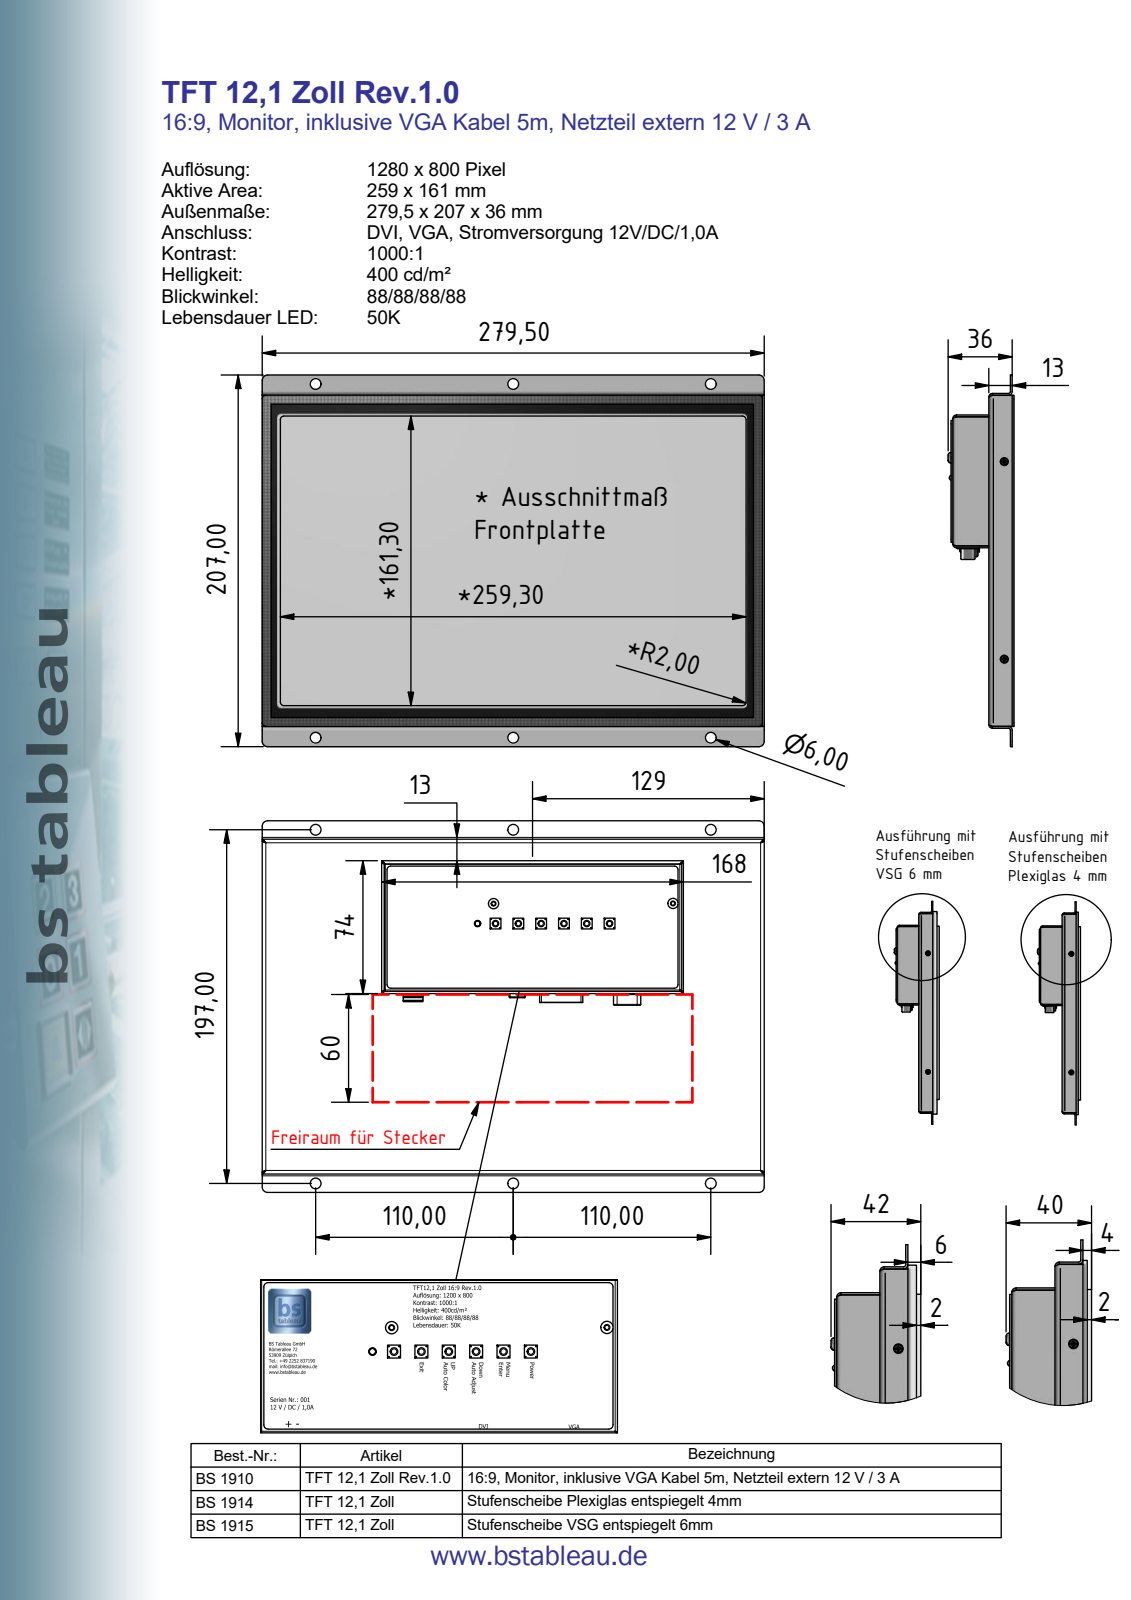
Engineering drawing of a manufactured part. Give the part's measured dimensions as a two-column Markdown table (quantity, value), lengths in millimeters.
| quantity | value |
| --- | --- |
| part name | 20000021 TFT 12,1 Zoll 16_9 Rev.1.0; 00003462 TDS 3165 - G121-1-L01 - MSC; 00000010 NB-4pol; 00000089 G121I1-L01 (+8 more) |
| STEP written by | Autodesk Inventor 2019 (AUTOMOTIVE_DESIGN) |
| units | millimeters |
| bodies | 72 solids, 2006 faces (1241 planar, 442 cylindrical, 323 other) |
| overall size | 279.5 × 207 × 36.65 |
| volume | 660 002 mm³ |
| surface area | 329 929 mm² |
| round holes (diameter × count) | 0.8 × 15, 2.46 × 12, 3.2 × 8, 5.41 × 8, 6 × 7, 1.57 × 2, 2.5 × 2, 2.6 × 2, 3.3 × 2, 3.4 × 2, 3.5 × 1 |
| round bosses / shafts (diameter × count) | 0.5 × 24, 3 × 9, 5.7 × 8, 5.42 × 8, 3.5 × 6, 8 × 2, 3.8 × 2, 2 × 2 |
| partial cylindrical surfaces (radius × count) | 0.1 × 172, 2 × 22, 0.5 × 20, 1 × 16, 4 × 16, 0.2 × 6, 0.8 × 6, 1.8 × 6 |
| main face-to-face distances | 1, 12, 10.5, 13, 2.5, 1.5, 21, 20, 33, 22.5 |
| hole center spacings | 2, 1.77, 4, 2.03, 3.18, 3.77, 0.5, 3.62 |
